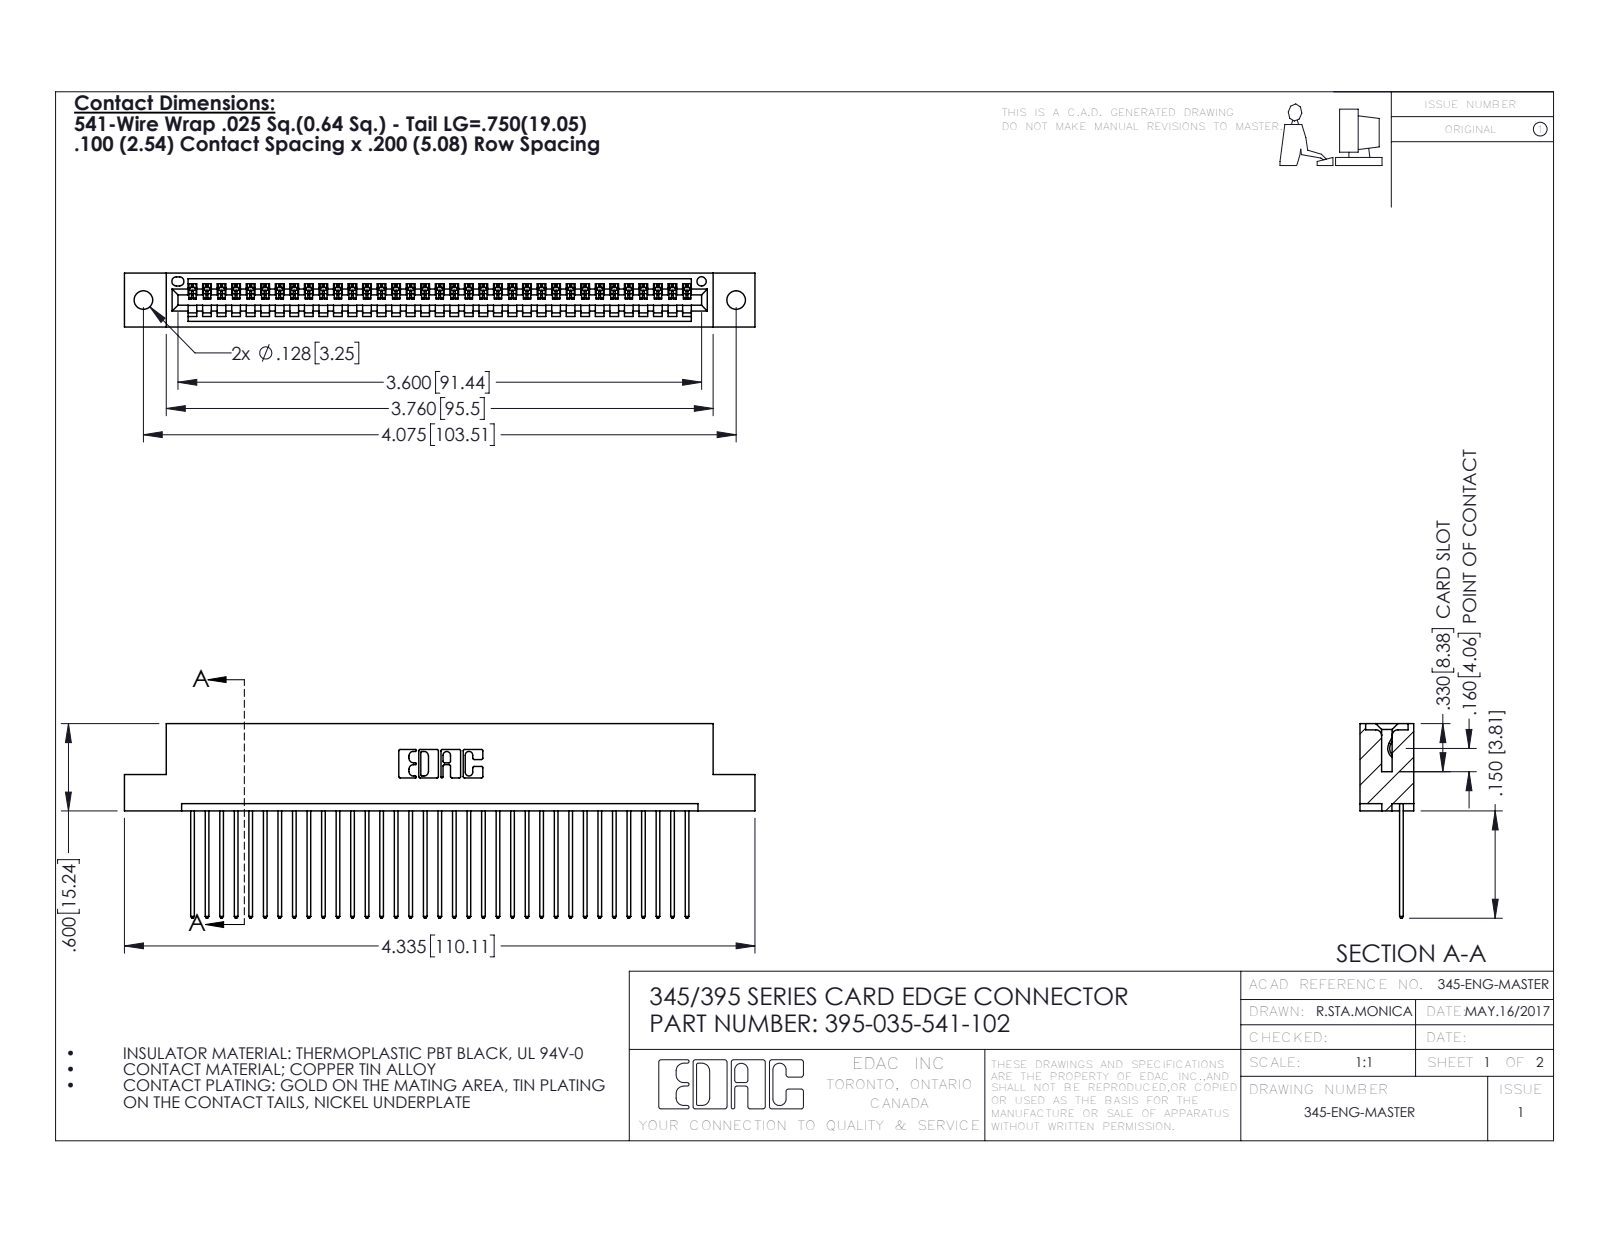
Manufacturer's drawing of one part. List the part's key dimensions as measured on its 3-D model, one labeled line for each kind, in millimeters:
Part name (STEP PRODUCT): 395-035-541-102; 345-292-001_345-293-141; 345 Part_Flush Mounting Lugs - 0.128 Dia
STEP written by: SolidWorks 2016 (CONFIG_CONTROL_DESIGN)
Units: millimetres
Bodies: 36 solids, 2156 faces (1480 planar, 676 cylindrical, 0 other)
Overall size (bounding box): 110.1 × 34 × 9.4
Volume: 10 500 mm³ · Surface area: 14 240 mm²
Round holes (diameter × count): ⌀3.3 ×2, ⌀1.6 ×1
Partial cylindrical surfaces — rounded edges, fillets, slot ends (radius × count): R0.2 ×70, R0.3 ×70, R0.3 ×22, R0.2 ×6, R0.8 ×6, R0.7 ×3, R0.8 ×2, R1 ×2
Main face-to-face distances: 1.8, 7.6, 2.5, 6.9, 0.6, 9.4, 5.1, 5.7, 3.8, 1.8
Hole centre spacings: 6.9, 97.5, 103.5
